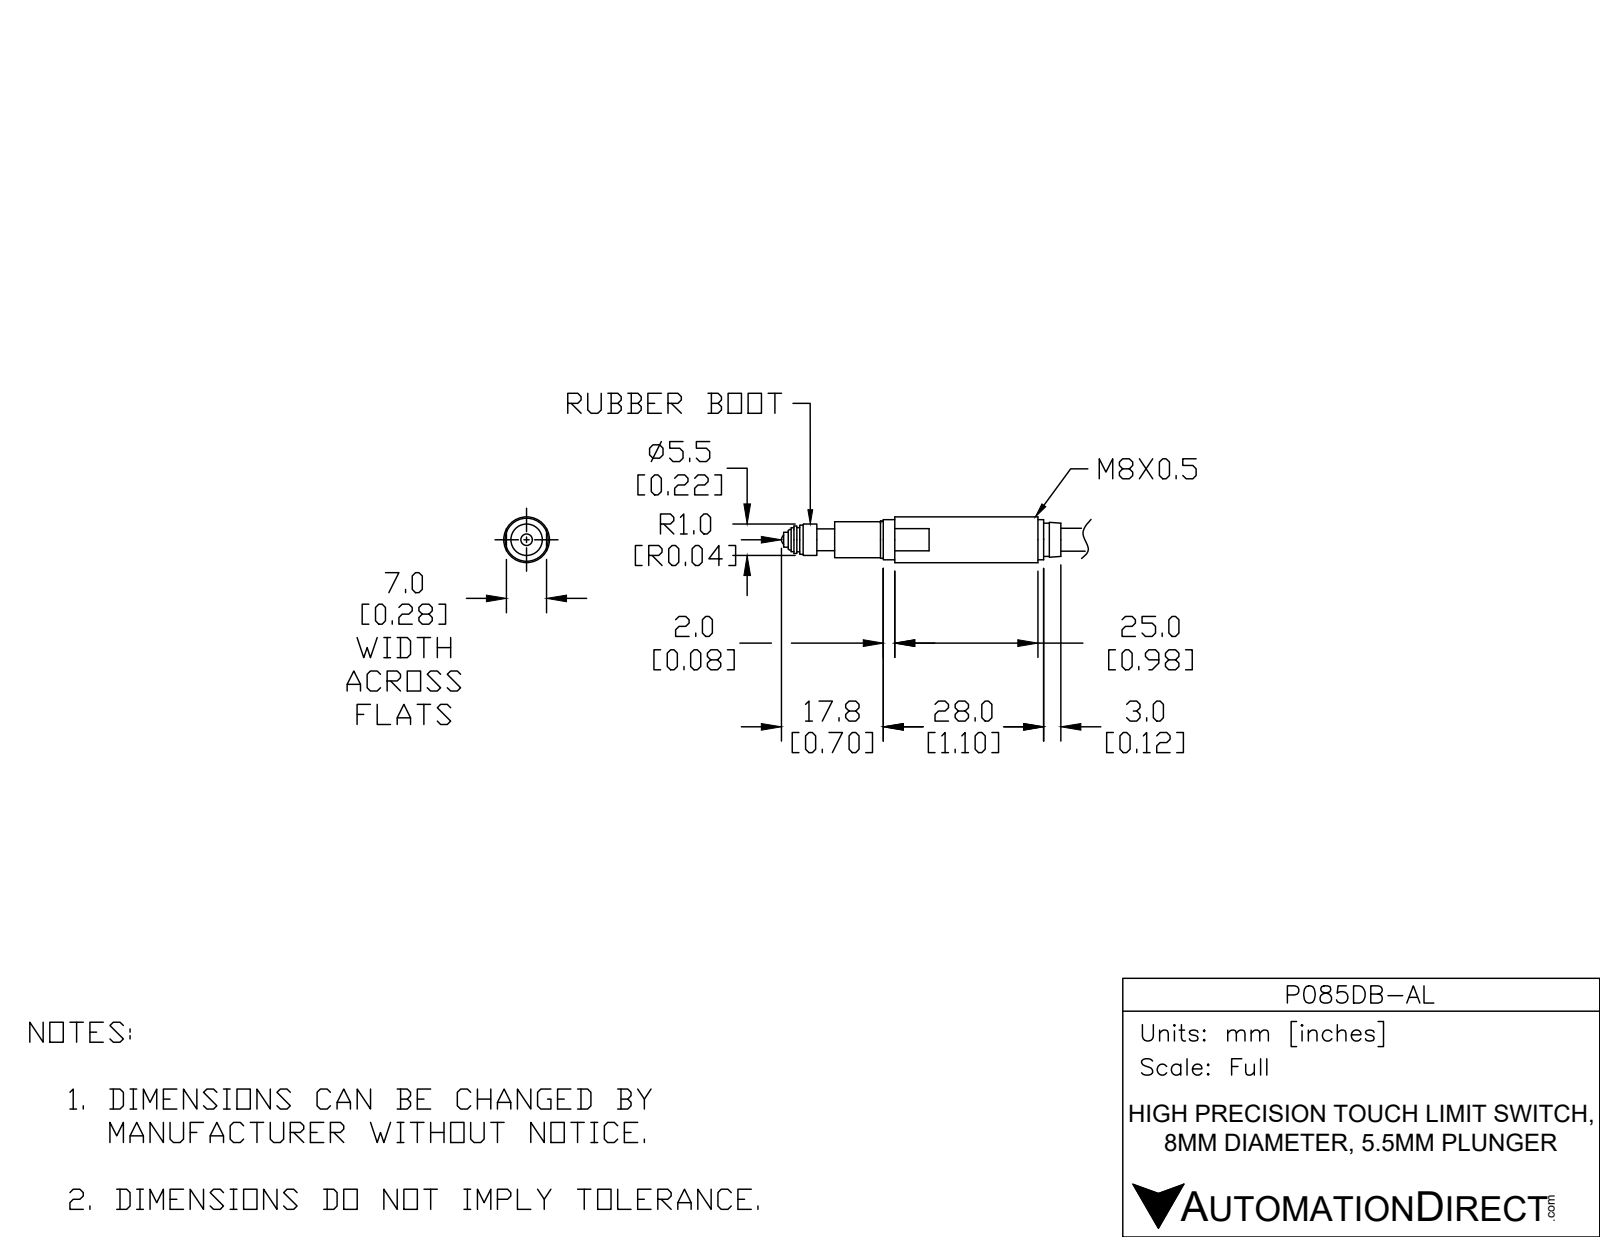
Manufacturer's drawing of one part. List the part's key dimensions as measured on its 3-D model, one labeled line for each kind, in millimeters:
Part name (STEP PRODUCT): P085DB-AL
STEP written by: SolidWorks 2017 (AUTOMOTIVE_DESIGN)
Units: millimetres
Bodies: 1 solid, 234 faces (22 planar, 129 cylindrical, 83 other)
Overall size (bounding box): 52.8 × 8 × 8
Volume: 1 800 mm³ · Surface area: 1 641 mm²
Round bosses / shafts (diameter × count): ⌀8 ×1, ⌀7 ×1, ⌀6.5 ×1, ⌀6.3 ×1, ⌀5.8 ×1, ⌀5.5 ×1, ⌀5.1 ×1, ⌀4.8 ×1
Main face-to-face distances: 7, 4, 42.6, 1, 3, 46.6, 0.5, 39.5, 2, 43.5
